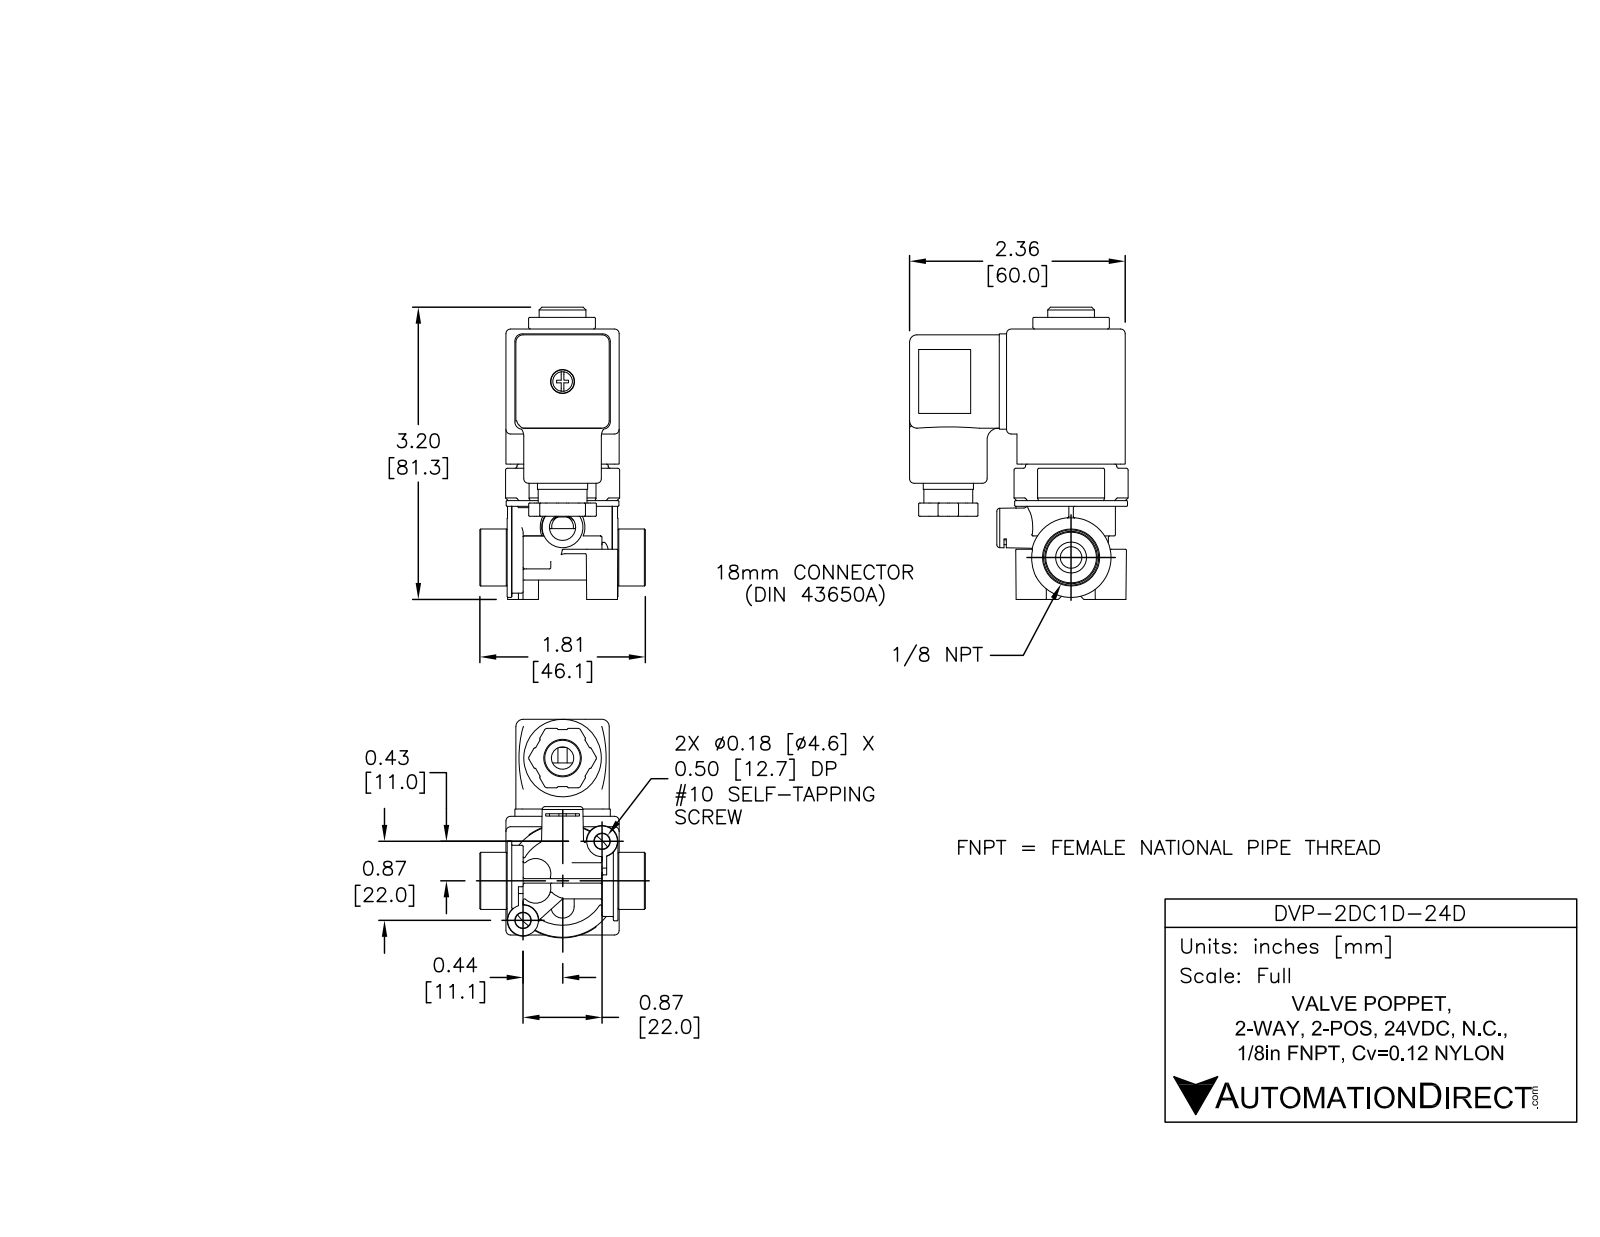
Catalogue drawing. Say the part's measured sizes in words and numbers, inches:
The part is named "DVP-2DC1D-24D". Its 3-D file was written by "SolidWorks 2015 (AUTOMOTIVE_DESIGN)". It is 9 solids with 2037 faces: 819 planar, 388 cylindrical and 830 other. Overall it measures 3.216 by 2.395 by 1.813 inches. Its volume is 4.043 cubic inches and its surface area 56.93 square inches. Round holes: 2 of diameter 0.06, 2 of diameter 0.236, 1 of diameter 0.08, 1 of diameter 0.102, 1 of diameter 0.12, 1 of diameter 0.203, 1 of diameter 0.245, 1 of diameter 0.263, 1 of diameter 0.287, 1 of diameter 0.339, 1 of diameter 0.37, 1 of diameter 0.375. Round bosses or shafts: 2 of diameter 0.29, 1 of diameter 1.236, 1 of diameter 1, 1 of diameter 0.972, 1 of diameter 0.922, 1 of diameter 0.89, 1 of diameter 0.875, 1 of diameter 0.85. Partial cylindrical surfaces (rounded edges, fillets, slot ends): 85 of radius 0.01, 50 of radius 0.015, 21 of radius 0.05, 12 of radius 0.02, 12 of radius 0.08, 6 of radius 0.026, 6 of radius 0.03, 4 of radius 0.04. The main face-to-face distances are 1.083, 1.24, 0.048, 0.157, 0.925, 1.48, 0.109, 1.131, 0.974, 1.367. The hole center spacings are 0.281, 0.283, 1.062, 1.343, 1.345, 1.612, 1.626, 2.184.
